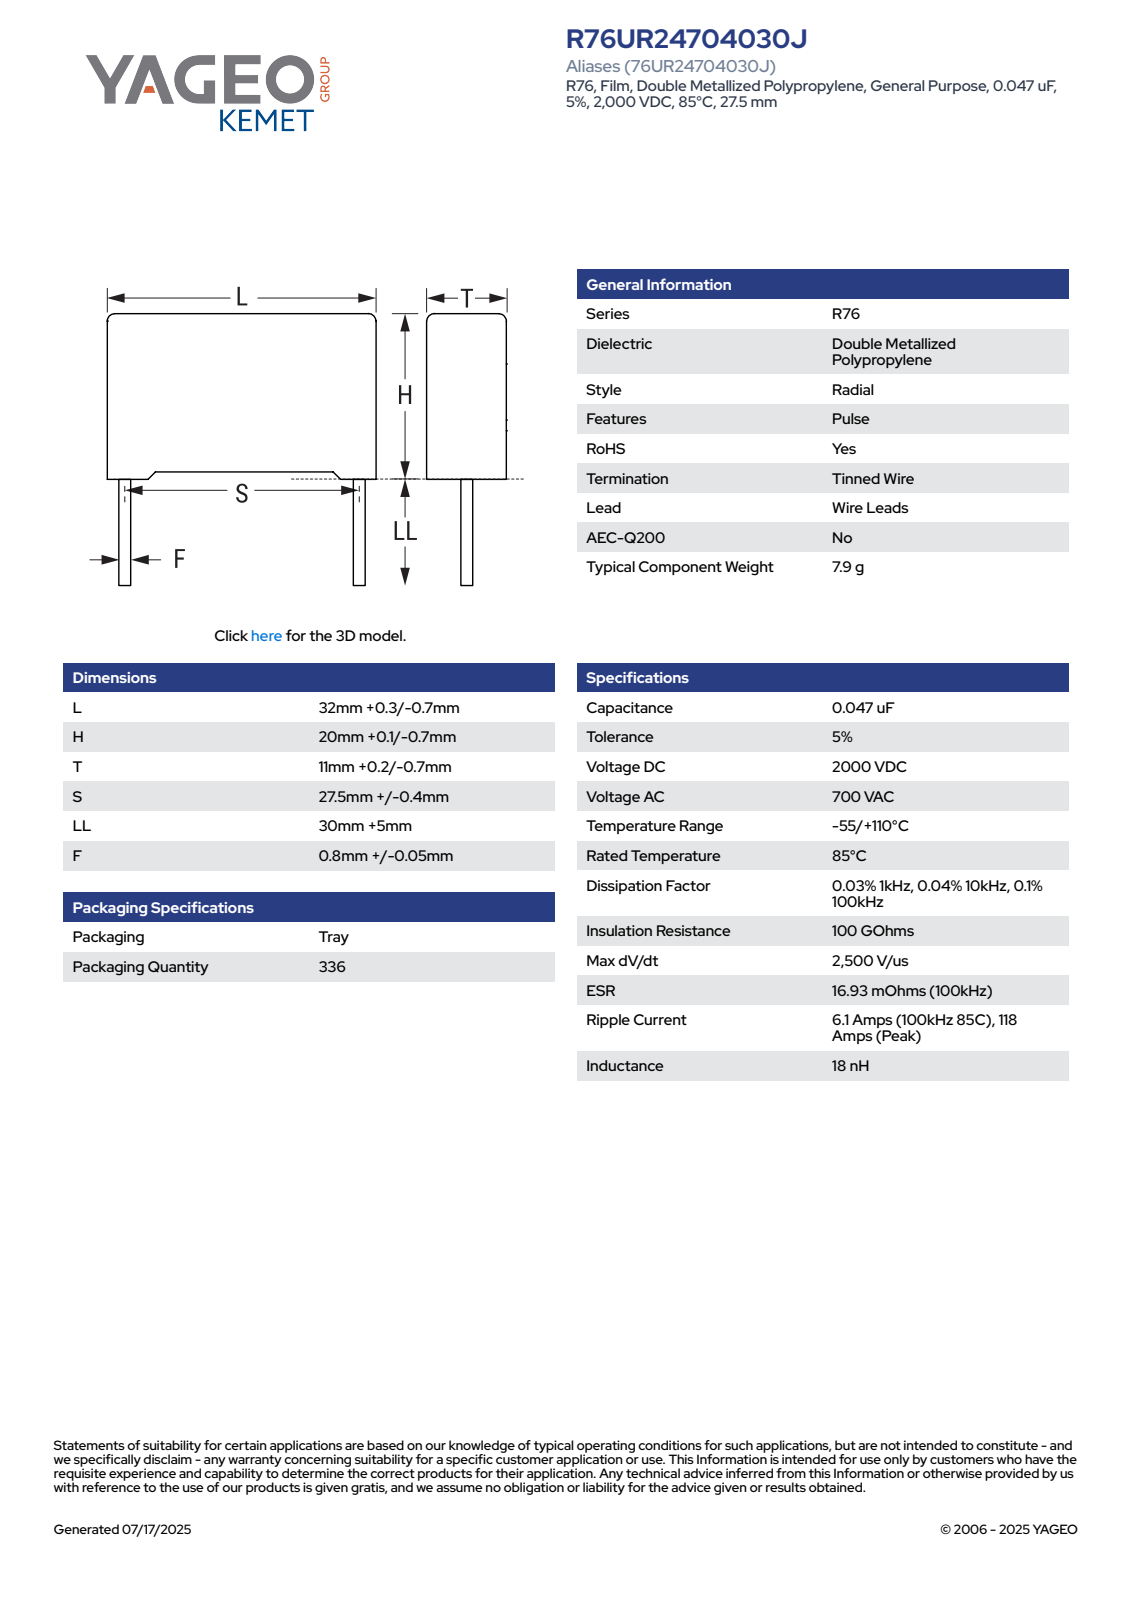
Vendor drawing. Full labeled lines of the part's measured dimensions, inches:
Part name (STEP PRODUCT): CFR_RB2_32X20X11_L32.3H20.1T11.2S27.5LL35F0.85
STEP written by: SolidWorks 2021 (AUTOMOTIVE_DESIGN)
Units: inches
Bodies: 4 solids, 85 faces (77 planar, 8 cylindrical, 0 other)
Overall size (bounding box): 2.169 × 1.272 × 0.441
Volume: 0.431 in³ · Surface area: 4.211 in²
Round bosses / shafts (diameter × count): ⌀0.033 ×2
Partial cylindrical surfaces — rounded edges, fillets, slot ends (radius × count): R0.02 ×4
Main face-to-face distances: 0.441, 0.762, 1.272, 0.764, 0.027, 0.03, 0.791, 0.043, 0.441, 1.229
